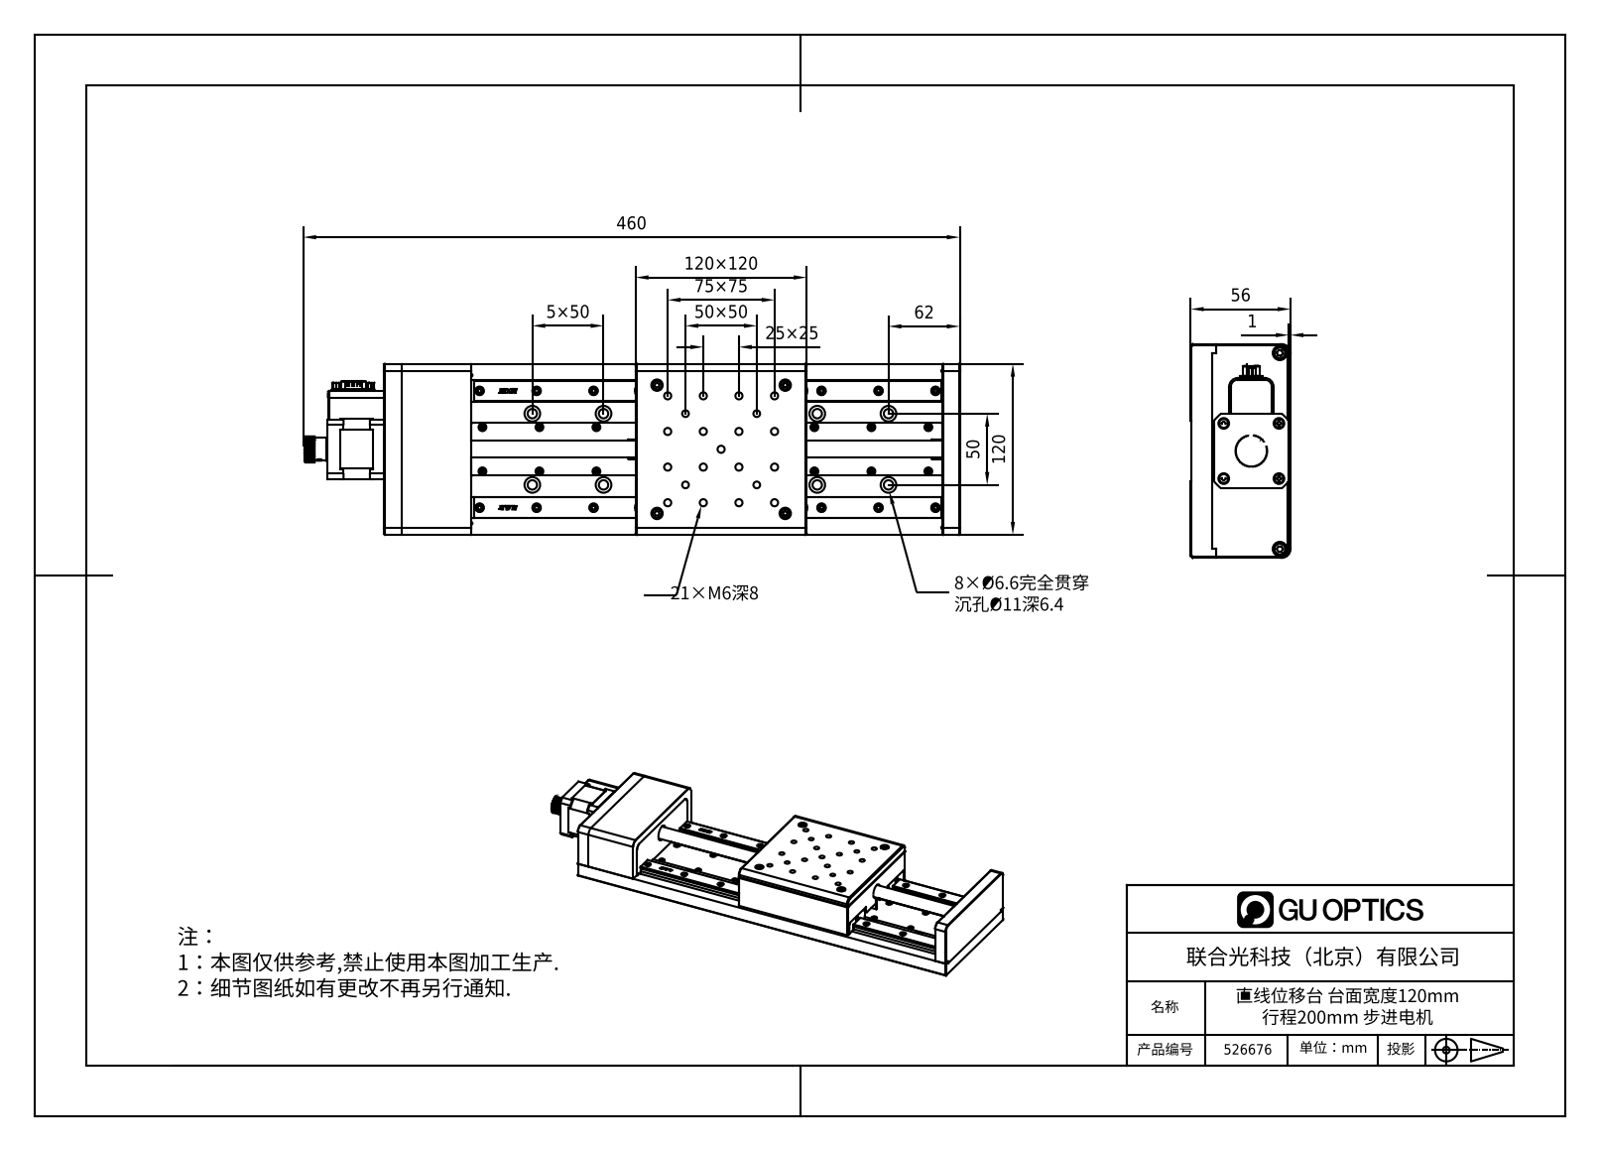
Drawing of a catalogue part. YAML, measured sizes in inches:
part_name: "FMS120-200"
step_written_by: "SolidWorks 2017 (CONFIG_CONTROL_DESIGN)"
units: inches
bodies: {solids: 0, faces: 1197, planar: 588, cylindrical: 370, other: 239}
overall_size: [18.094, 4.724, 2.205]
round_holes:
  - {diameter: 0.197, count: 17}
  - {diameter: 0.236, count: 16}
  - {diameter: 0.315, count: 14}
  - {diameter: 0.26, count: 12}
  - {diameter: 0.433, count: 8}
  - {diameter: 0.079, count: 5}
  - {diameter: 0.185, count: 4}
  - {diameter: 0.098, count: 2}
  - {diameter: 0.177, count: 2}
  - {diameter: 0.551, count: 1}
round_bosses_or_shafts:
  - {diameter: 0.173, count: 12}
  - {diameter: 0.039, count: 9}
  - {diameter: 0.217, count: 4}
  - {diameter: 0.165, count: 2}
  - {diameter: 0.63, count: 1}
  - {diameter: 0.472, count: 1}
  - {diameter: 0.276, count: 1}
partial_cylinders:
  - {radius: 0.02, count: 23}
  - {radius: 0.039, count: 12}
  - {radius: 0.012, count: 8}
  - {radius: 0.016, count: 7}
  - {radius: 0.197, count: 6}
  - {radius: 0.059, count: 4}
  - {radius: 0.354, count: 1}
  - {radius: 0.787, count: 1}
face_to_face_distances: [0.551, 1.339, 0.315, 1.102, 4.724, 1.89, 0.539, 1.878, 1.654, 2.205]
hole_center_spacings: [1.969, 2.784, 3.937, 4.402, 5.906, 6.225, 0.863, 1.22]
